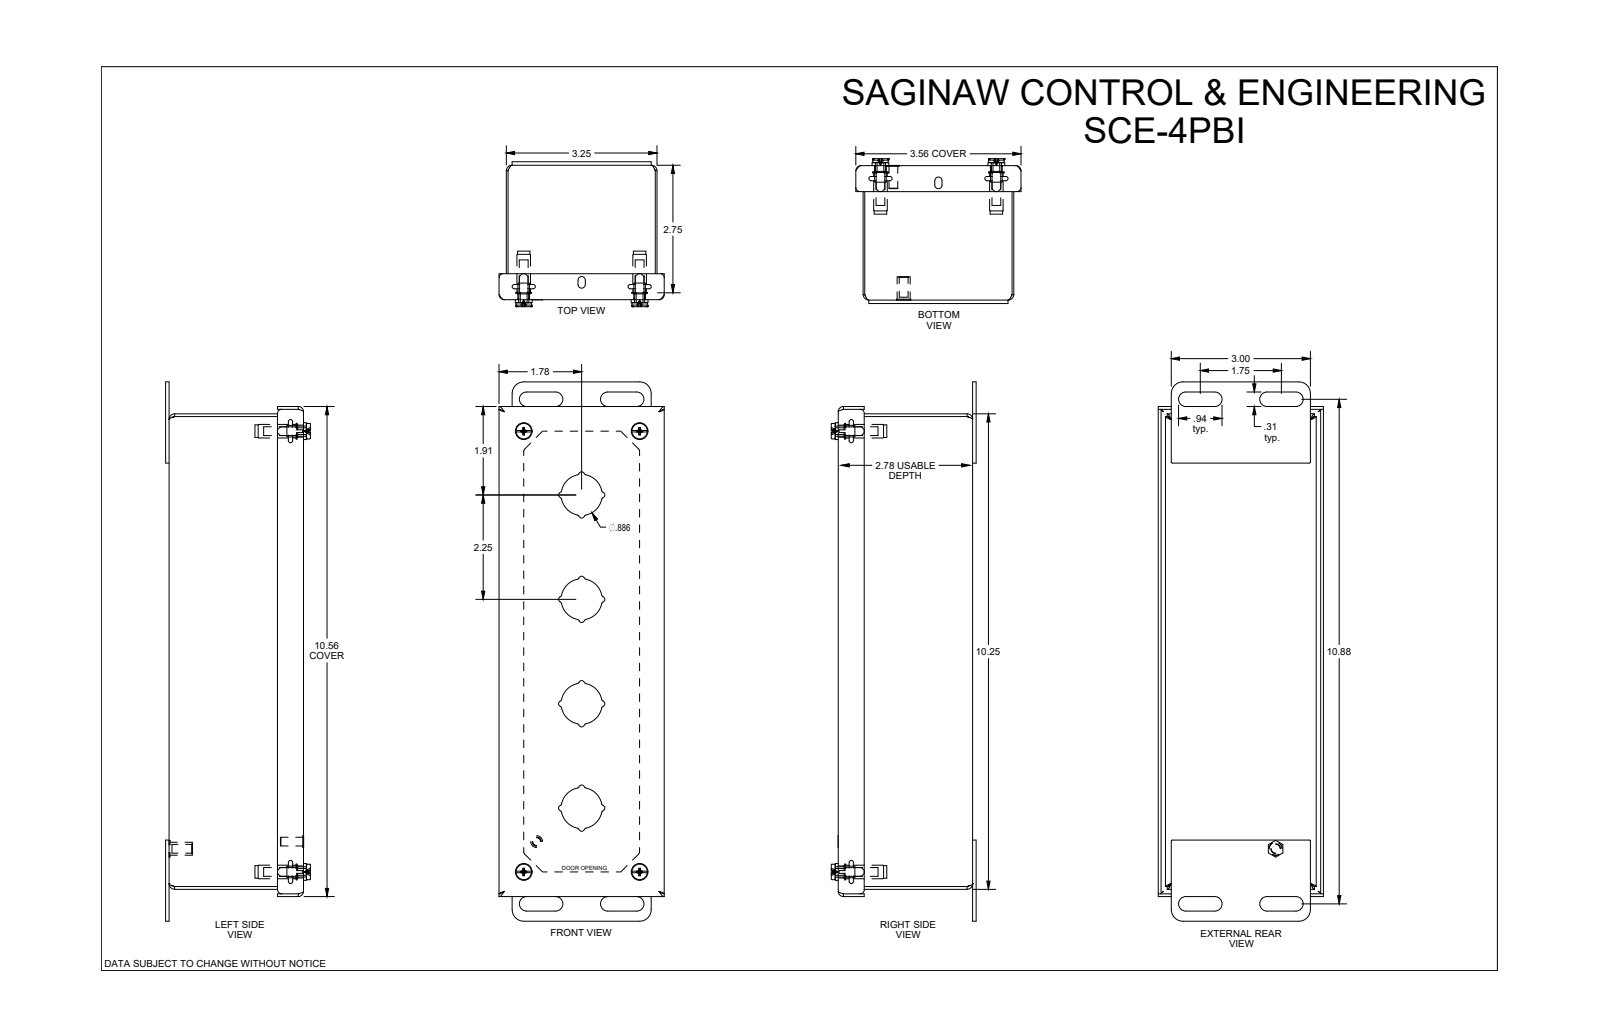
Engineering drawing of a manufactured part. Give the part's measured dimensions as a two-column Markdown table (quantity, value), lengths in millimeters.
| quantity | value |
| --- | --- |
| part name | SCE-4PBI |
| STEP written by | SolidWorks 2021 (AUTOMOTIVE_DESIGN) |
| units | millimeters |
| bodies | 3 solids, 480 faces (153 planar, 243 cylindrical, 84 other) |
| overall size | 295.3 × 90.5 × 77.1 |
| volume | 182 600 mm³ |
| surface area | 231 400 mm² |
| round holes (diameter × count) | 4.8 × 5, 5.6 × 4, 6.4 × 4, 6.8 × 4, 8.1 × 4 |
| round bosses / shafts (diameter × count) | 9.2 × 4, 8.6 × 4, 7.4 × 4, 6.9 × 4, 6.6 × 4, 7.1 × 1, 6.5 × 1, 4.8 × 1 |
| partial cylindrical surfaces (radius × count) | 1 × 32, 1.5 × 20, 1.6 × 16, 0.4 × 8, 2.9 × 8, 4 × 8, 6.2 × 8, 0.5 × 4 |
| main face-to-face distances | 1.5, 72.1, 81, 70.6, 73.6, 4, 82.6, 79.5, 85, 258.8 |
| hole center spacings | 249.5, 63.5, 241.3, 18, 63.5, 63.5, 234.2, 241.3 |
